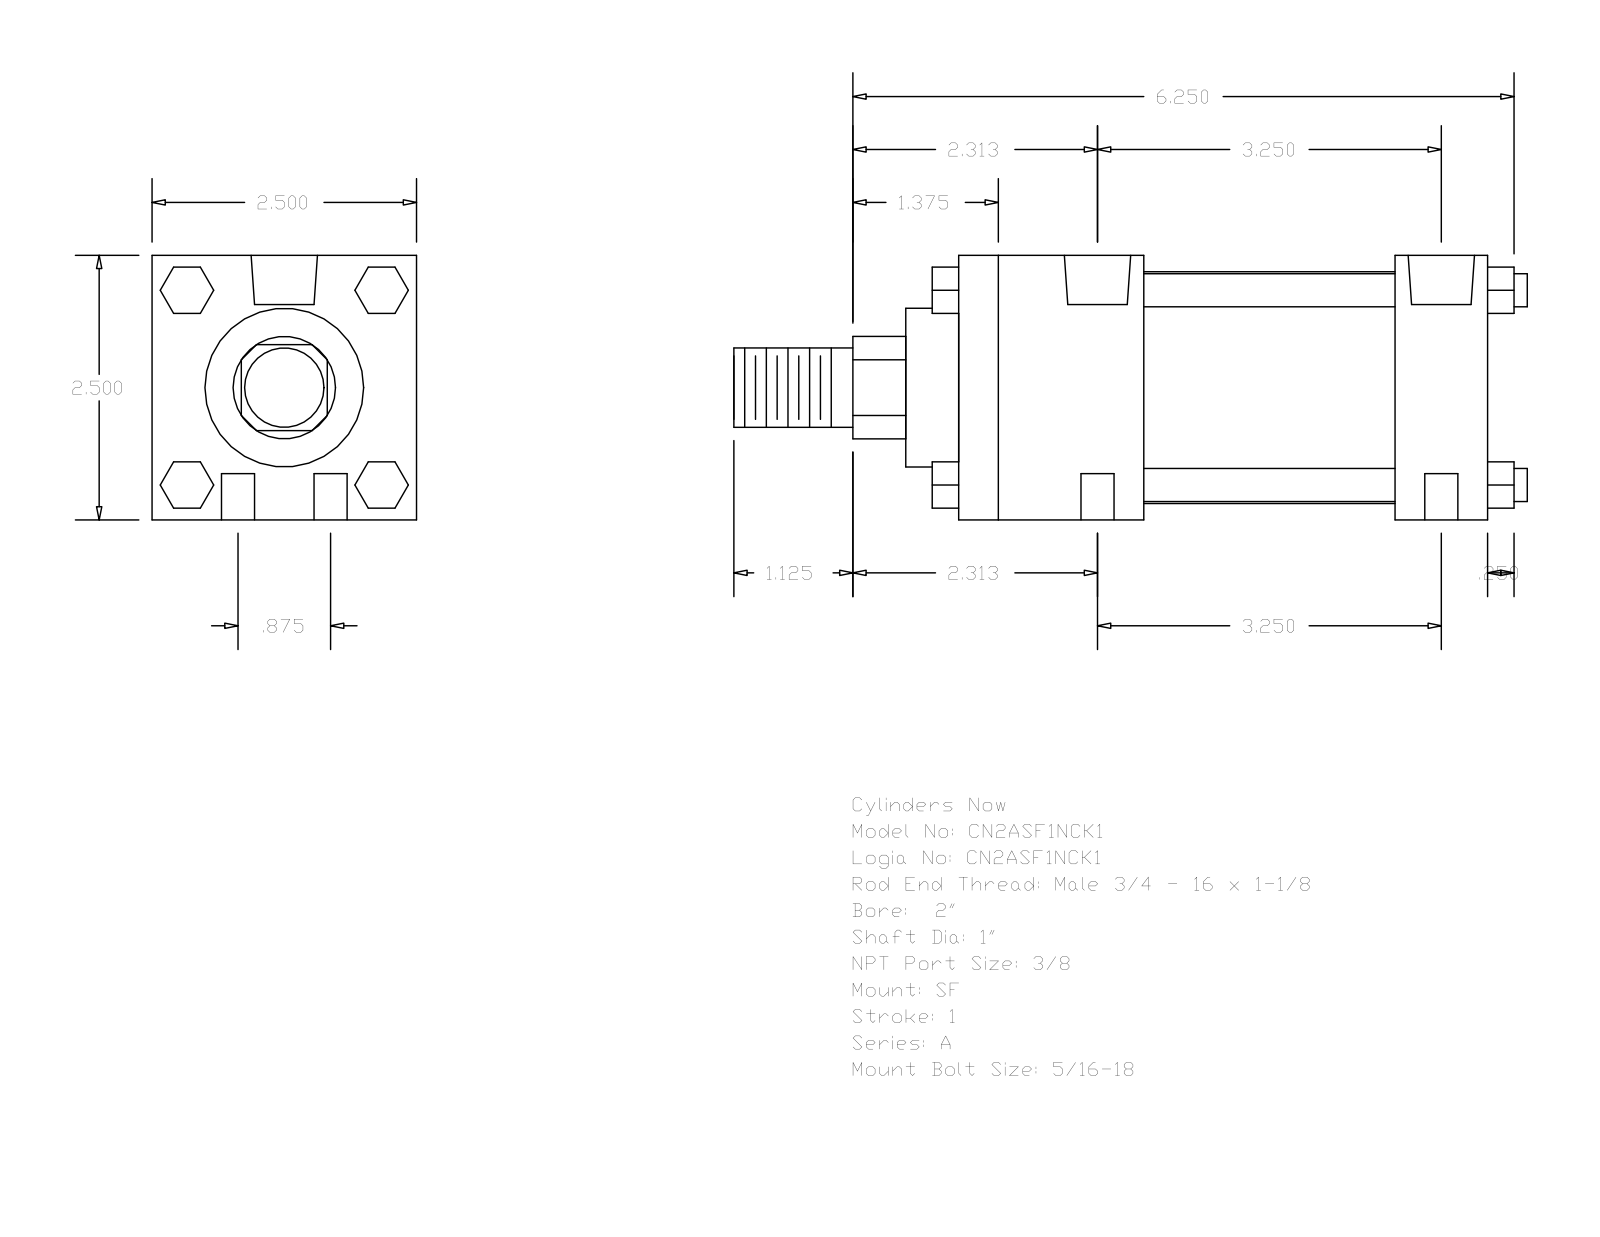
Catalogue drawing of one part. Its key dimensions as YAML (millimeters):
part_name: "A_SF__0200_1"
step_written_by: "GSSL Pune (CONFIG_CONTROL_DESIGN)"
units: millimeters
bodies: {solids: 0, faces: 124, planar: 94, cylindrical: 30, other: 0}
overall_size: [190.5, 63.5, 63.5]
round_holes:
  - {diameter: 7.94, count: 4}
  - {diameter: 5.56, count: 2}
  - {diameter: 15.93, count: 2}
round_bosses_or_shafts:
  - {diameter: 7.94, count: 4}
  - {diameter: 55.63, count: 1}
  - {diameter: 38.1, count: 1}
  - {diameter: 25.4, count: 1}
  - {diameter: 19.05, count: 1}
partial_cylinders:
  - {radius: 12.29, count: 1}
face_to_face_distances: [63.5, 127, 104.78, 22.22, 44.45, 60.33, 82.55, 12.7, 139.7, 6.35]
hole_center_spacings: [11.11, 83.29, 82.55, 22.22, 85.49, 76.98]
